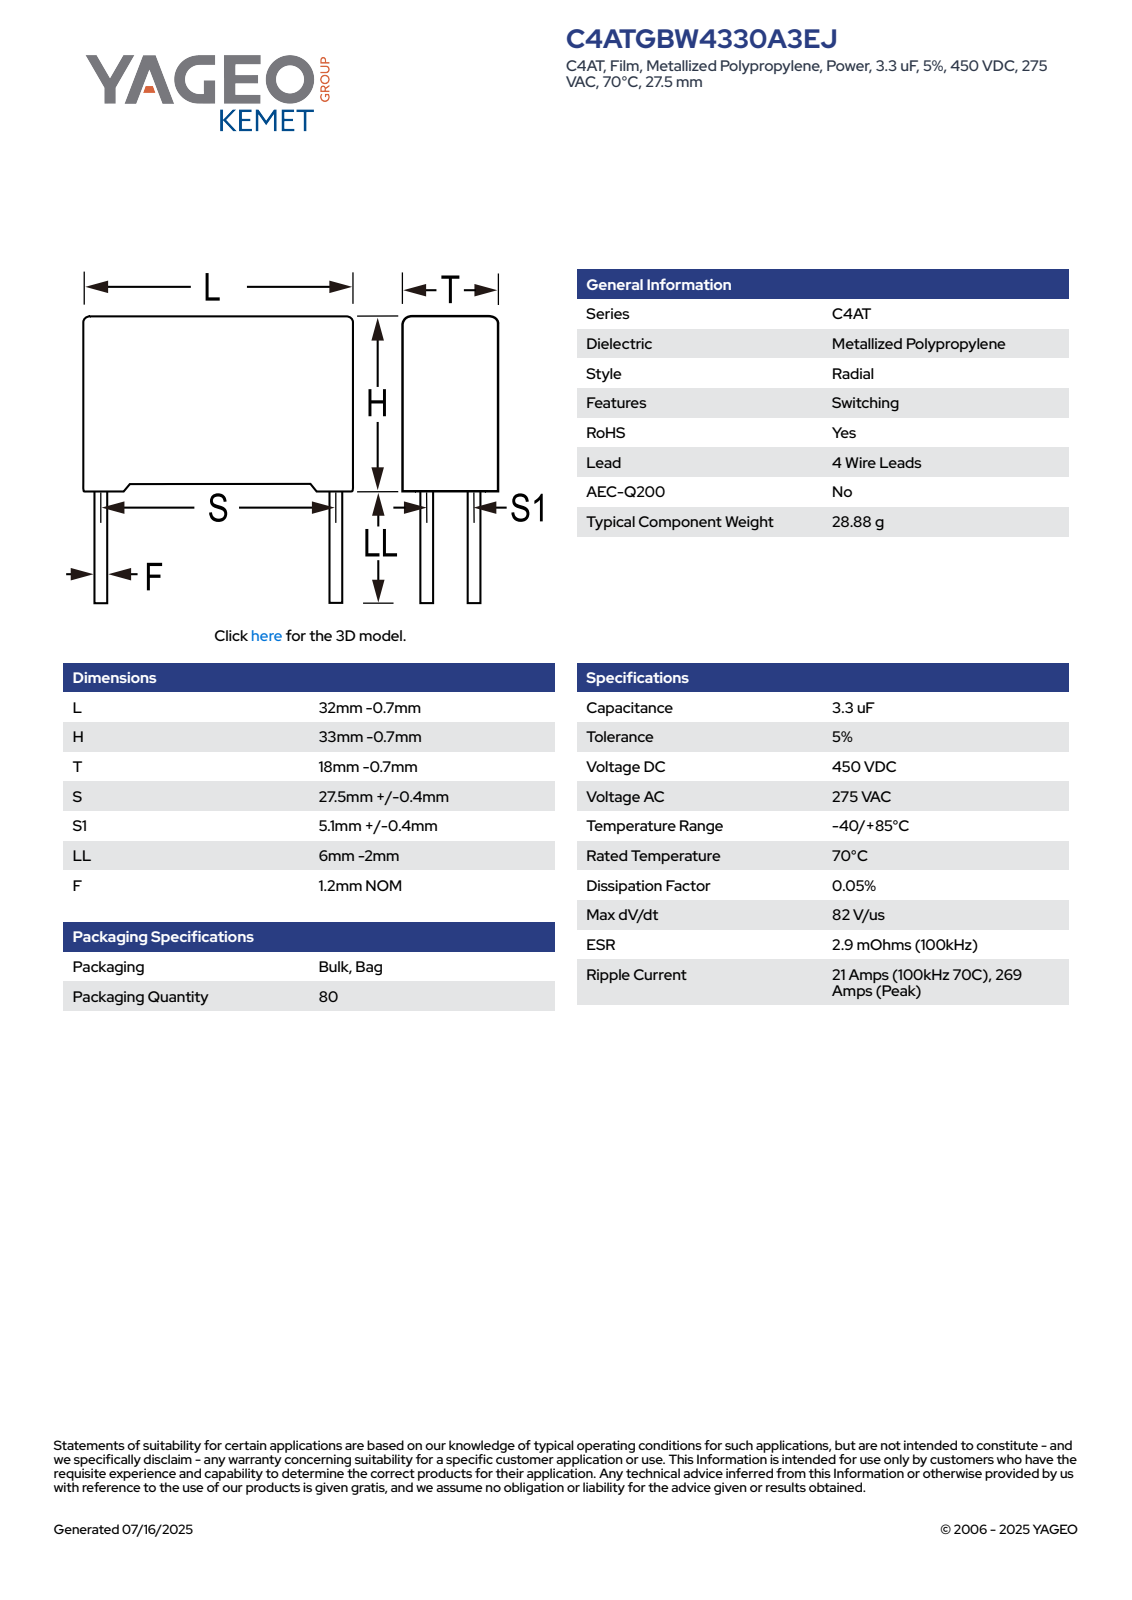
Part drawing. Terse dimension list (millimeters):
name: CFP_RB4_32X33X18_L31.3H32.3T17.3S27.5S15.1LL4F1.2
written by: SolidWorks 2014 (AUTOMOTIVE_DESIGN)
unit: mm
bodies: 4 solids, 87 faces (79 planar, 8 cylindrical, 0 other)
size: 36.3 × 31.3 × 17.3
volume: 17 056 mm³; area: 4 379 mm²
bosses: 4× ⌀1.2
face distances: 17.3, 31.3, 31.35, 0.95, 32.3, 1.06, 30.24, 16.24, 29.18, 15.18
